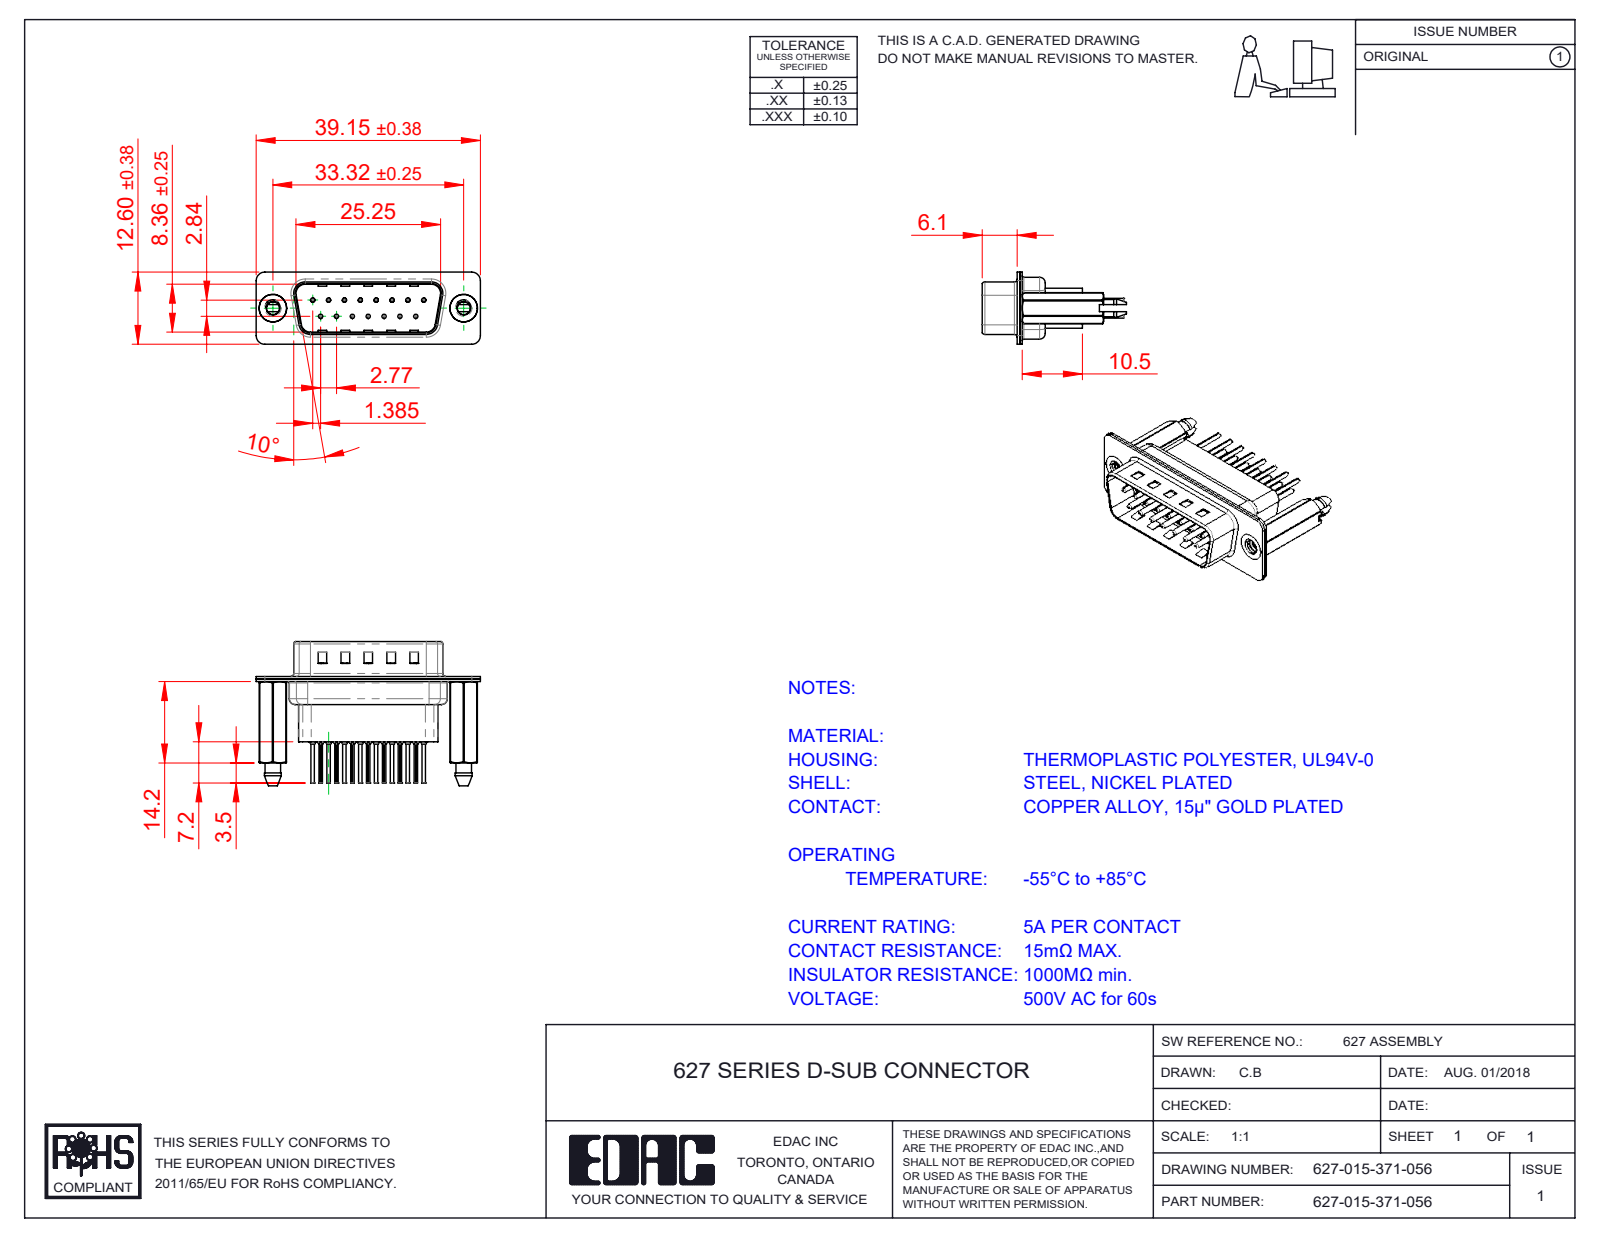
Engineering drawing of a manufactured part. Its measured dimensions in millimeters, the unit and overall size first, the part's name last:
Units: millimetres
Overall size (bounding box): 39.15 × 25.1 × 12.6
Round holes (diameter × count): ⌀0.2 ×15, ⌀0.35 ×15, ⌀1.1 ×15, ⌀1.6 ×15, ⌀2.26 ×2, ⌀4 ×2, ⌀4.8 ×2
Round bosses / shafts (diameter × count): ⌀2 ×15, ⌀1.5 ×15, ⌀0.75 ×15, ⌀0.6 ×15, ⌀4.9 ×2
Partial cylindrical surfaces — rounded edges, fillets, slot ends (radius × count): R0.1 ×30, R1.5 ×18, R2 ×12, R1.6 ×10, R0.5 ×8, R0.25 ×4, R0.6 ×4, R0.65 ×4
Main face-to-face distances: 0.4, 0.45, 0.9, 0.82, 9.58, 4.76, 1.5, 0.68, 7.68, 1.4
Hole centre spacings: 3.16, 2.77, 5.54, 8.31, 11.08, 5.03, 5.04, 7.48
Volume: 2 911 mm³ · Surface area: 7 517 mm²
Bodies: 20 solids, 1918 faces (531 planar, 754 cylindrical, 633 other)
Part name (STEP PRODUCT): 627 Housing_15 HP; 627-015-371-056; 627 Contact Row 1_61; 627 Contact Row 2_61 (+3 more)
STEP written by: SolidWorks 2020 (CONFIG_CONTROL_DESIGN)
